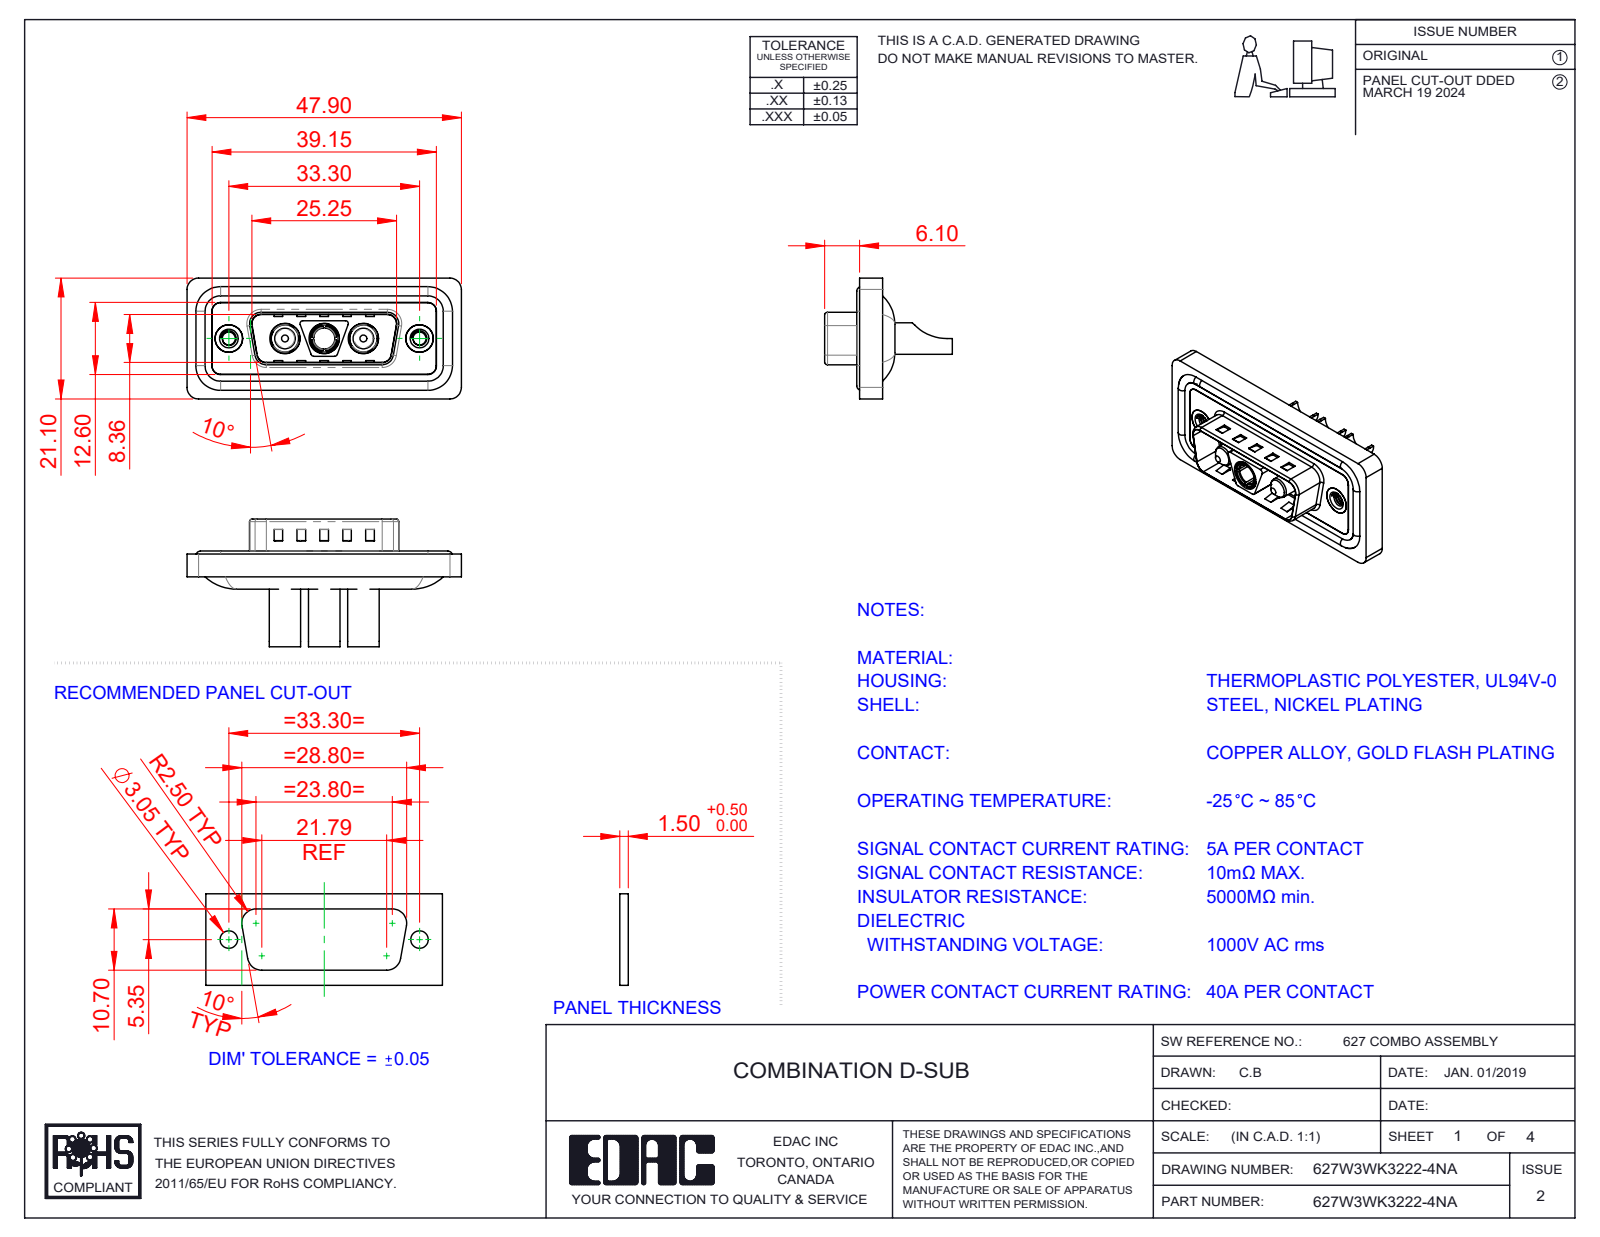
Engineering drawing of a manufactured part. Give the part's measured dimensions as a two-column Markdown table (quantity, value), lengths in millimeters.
| quantity | value |
| --- | --- |
| part name | 627Combo Shell Front_15 Contacts; 627Combo Waterproof Housing_15 Contacts; 627W3WK3222-4NA; 627Combo Threaded Rivet_A (+4 more) |
| STEP written by | SolidWorks 2023 (CONFIG_CONTROL_DESIGN) |
| units | millimeters |
| bodies | 13 solids, 619 faces (237 planar, 255 cylindrical, 127 other) |
| overall size | 47.9 × 22.3 × 21.1 |
| volume | 5 809 mm³ |
| surface area | 9 544 mm² |
| round holes (diameter × count) | 4.6 × 3, 4.85 × 3, 5.3 × 3, 2.26 × 2, 4 × 2, 4.8 × 2, 5 × 2, 3.7 × 1 |
| round bosses / shafts (diameter × count) | 1.6 × 4, 5.5 × 3, 5.2 × 3, 4.75 × 3, 3.75 × 3, 4.9 × 2, 3.6 × 2, 4.96 × 1 |
| partial cylindrical surfaces (radius × count) | 1.5 × 26, 2 × 20, 0.5 × 12, 1.6 × 8, 0.25 × 4, 0.6 × 4, 0.65 × 4, 0.9 × 4 |
| main face-to-face distances | 0.4, 1.1, 0.5, 1.6, 3.1, 2.9, 1.5, 0.82, 9.58, 2.5 |
| hole center spacings | 6.85, 9.8, 16.65, 23.5, 13.7, 33.3 |
